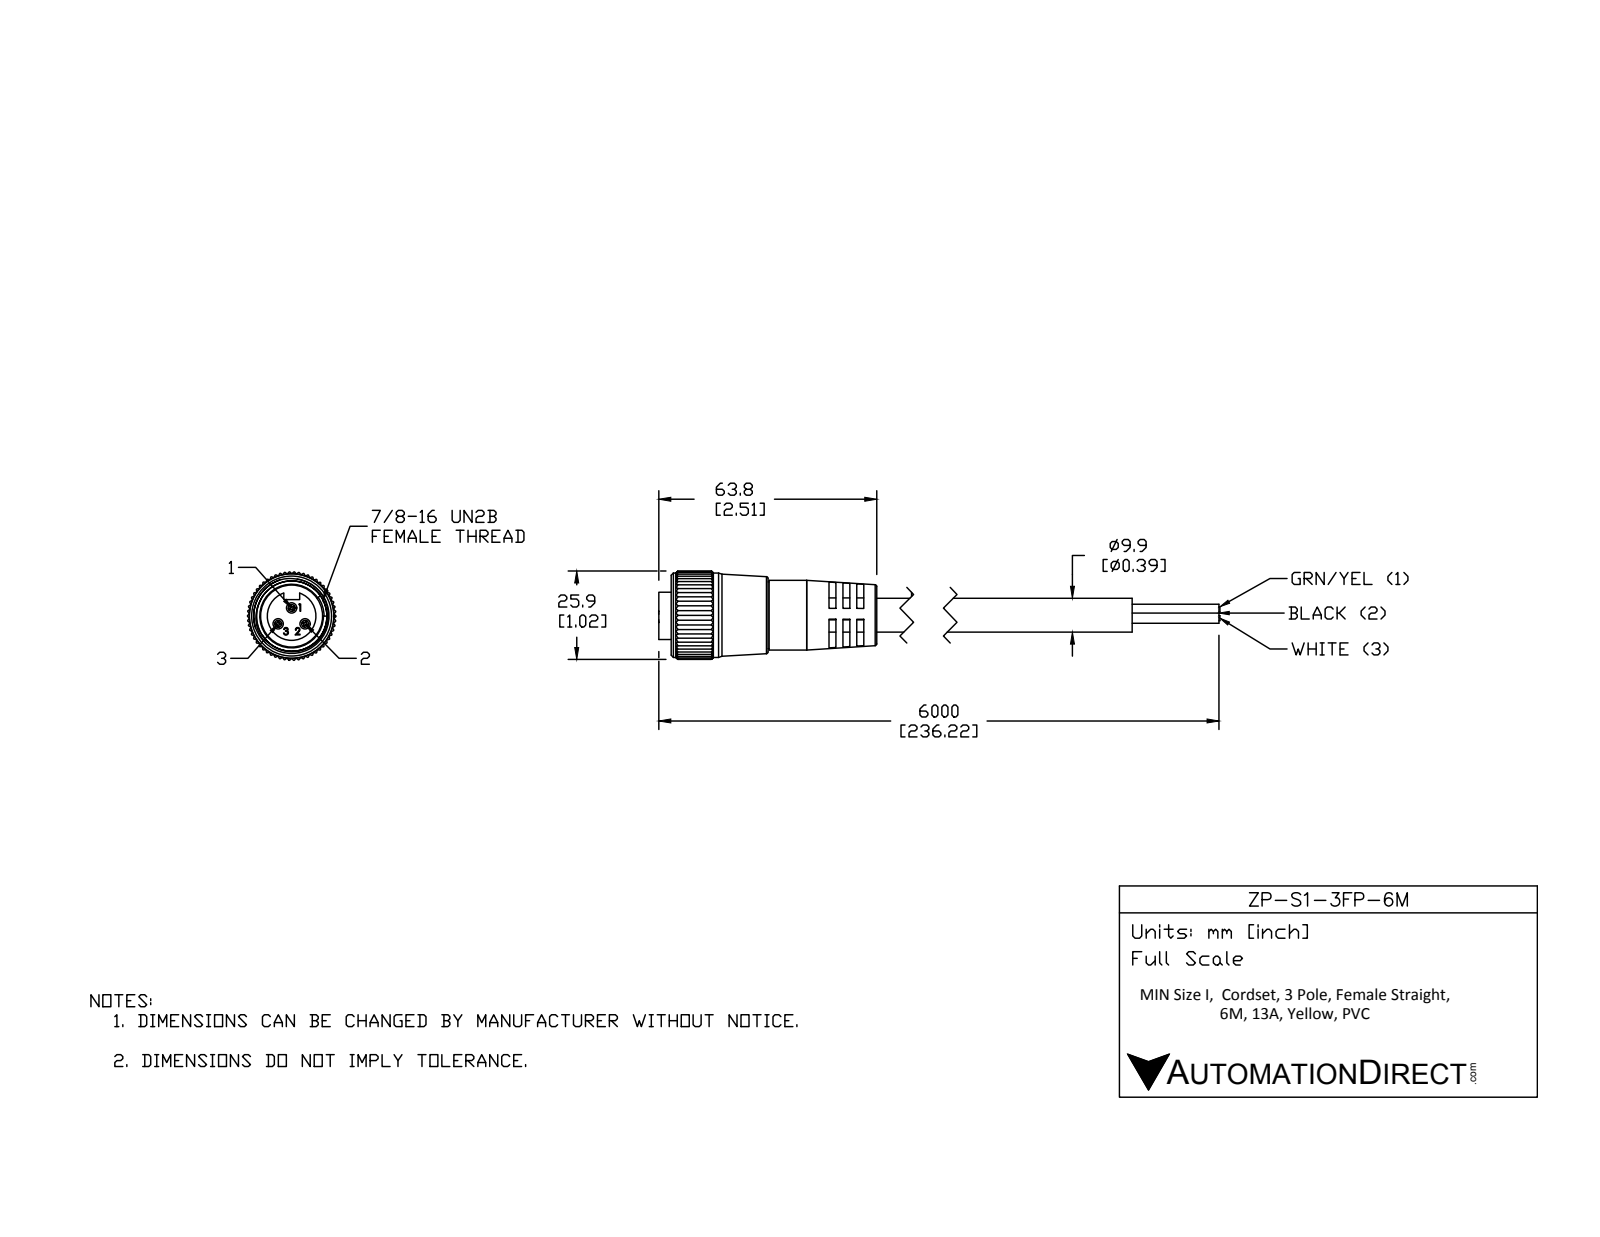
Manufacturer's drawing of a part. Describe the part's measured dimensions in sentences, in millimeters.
The part is named "ZP-S1-3FP-6M". Its 3-D file was written by "SolidWorks 2015 (AUTOMOTIVE_DESIGN)". It is 2 solids with 540 faces: 192 planar, 306 cylindrical and 42 other. Overall it measures 108.72 by 52.91 by 25.84 millimeters. Its volume is 26 739 cubic millimeters and its surface area 11 837 square millimeters. Round holes: 3 of diameter 3.05, 1 of diameter 18.14, 1 of diameter 20.58, 1 of diameter 21. Round bosses or shafts: 2 of diameter 9.91, 1 of diameter 24.68, 1 of diameter 20.4, 1 of diameter 19.5, 1 of diameter 14.22. Partial cylindrical surfaces (rounded edges, fillets, slot ends): 165 of radius 0.25, 1 of radius 5.25, 1 of radius 12.93. The main face-to-face distances are 4.03, 2, 2.03, 6.03, 8.06, 13.87, 11.87, 9.84, 7.84, 6.06. The hole center spacings are 6.07, 2.36, 4.53, 4.54, 7.87.
